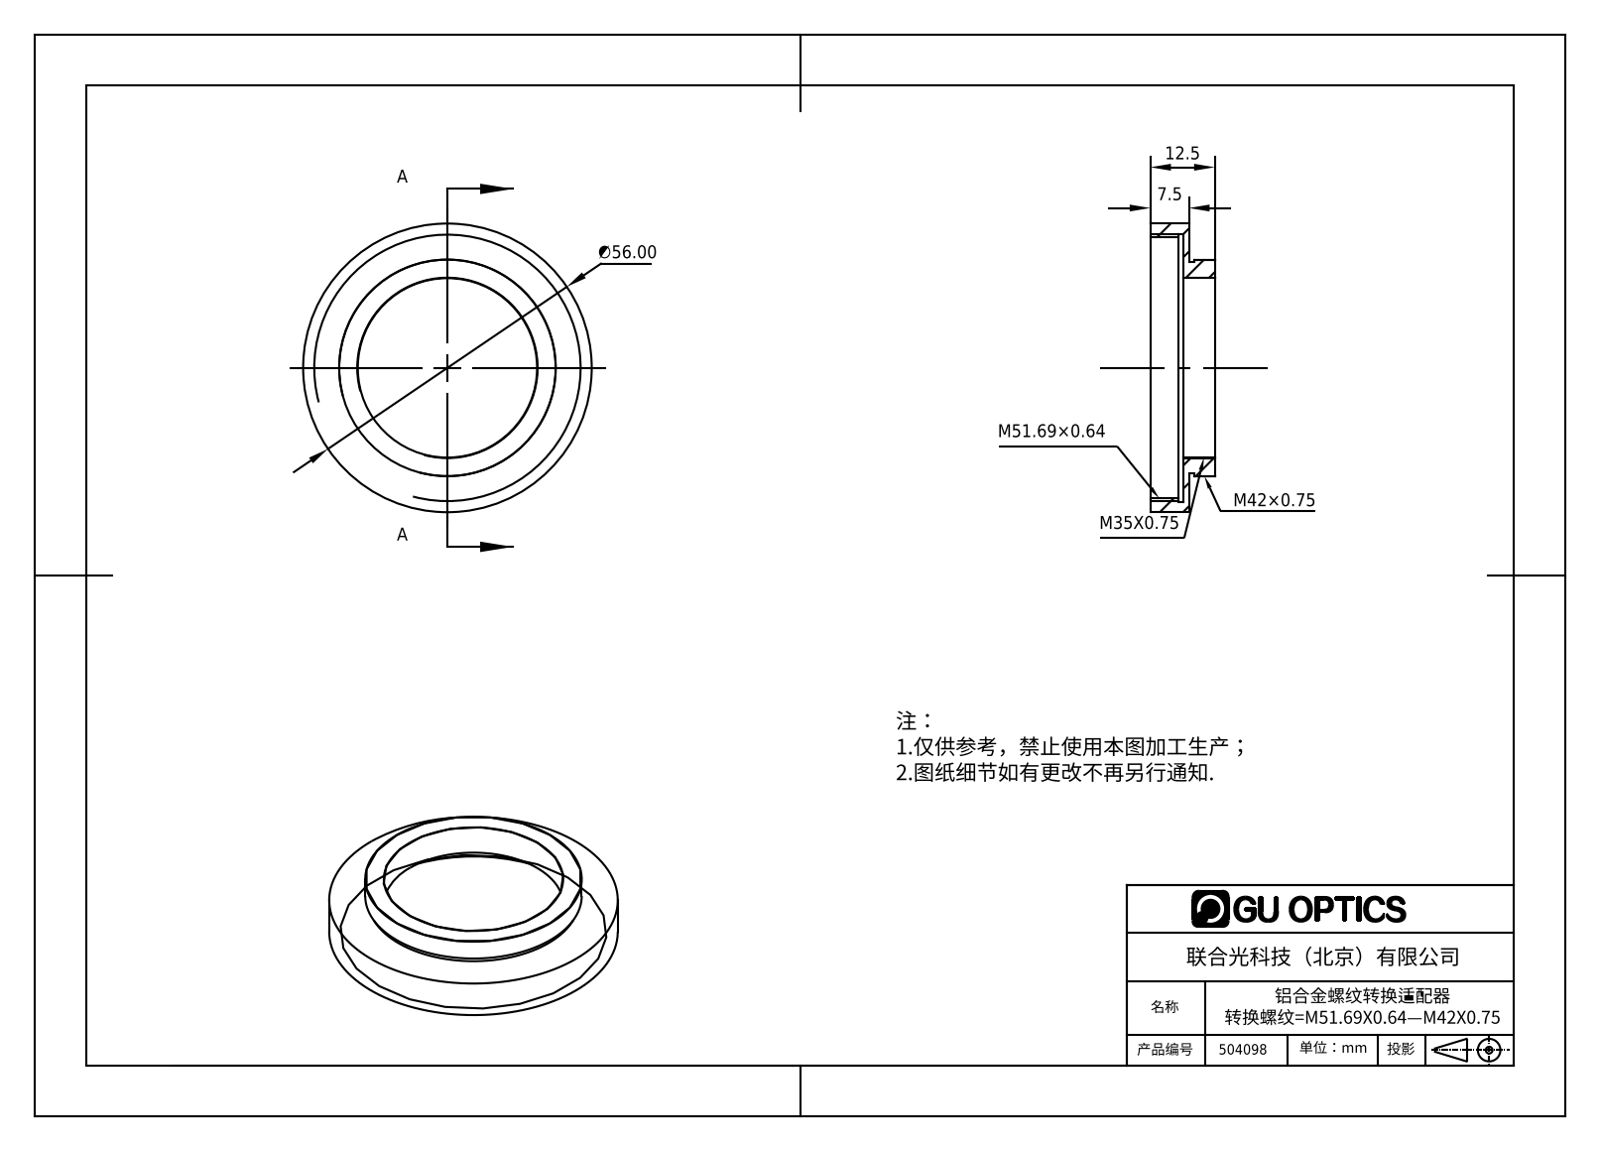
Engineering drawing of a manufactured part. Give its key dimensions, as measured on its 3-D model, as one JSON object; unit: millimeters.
{"part_name": "504098", "step_written_by": "SolidWorks 2016 (AUTOMOTIVE_DESIGN)", "units": "millimeters", "bodies": {"solids": 1, "faces": 18, "planar": 6, "cylindrical": 12, "other": 0}, "overall_size": [56, 56, 12.5], "volume_mm3": 6457, "surface_area_mm2": 7036, "round_holes": [[34.8, 1], [50.6, 1], [51.9, 1]], "round_bosses_or_shafts": [[56, 1], [42.02, 1], [41, 1]], "face_to_face_distances": [1, 6.5, 7.5, 12.5, 6, 5, 2, 5.5, 7, 8.5]}
